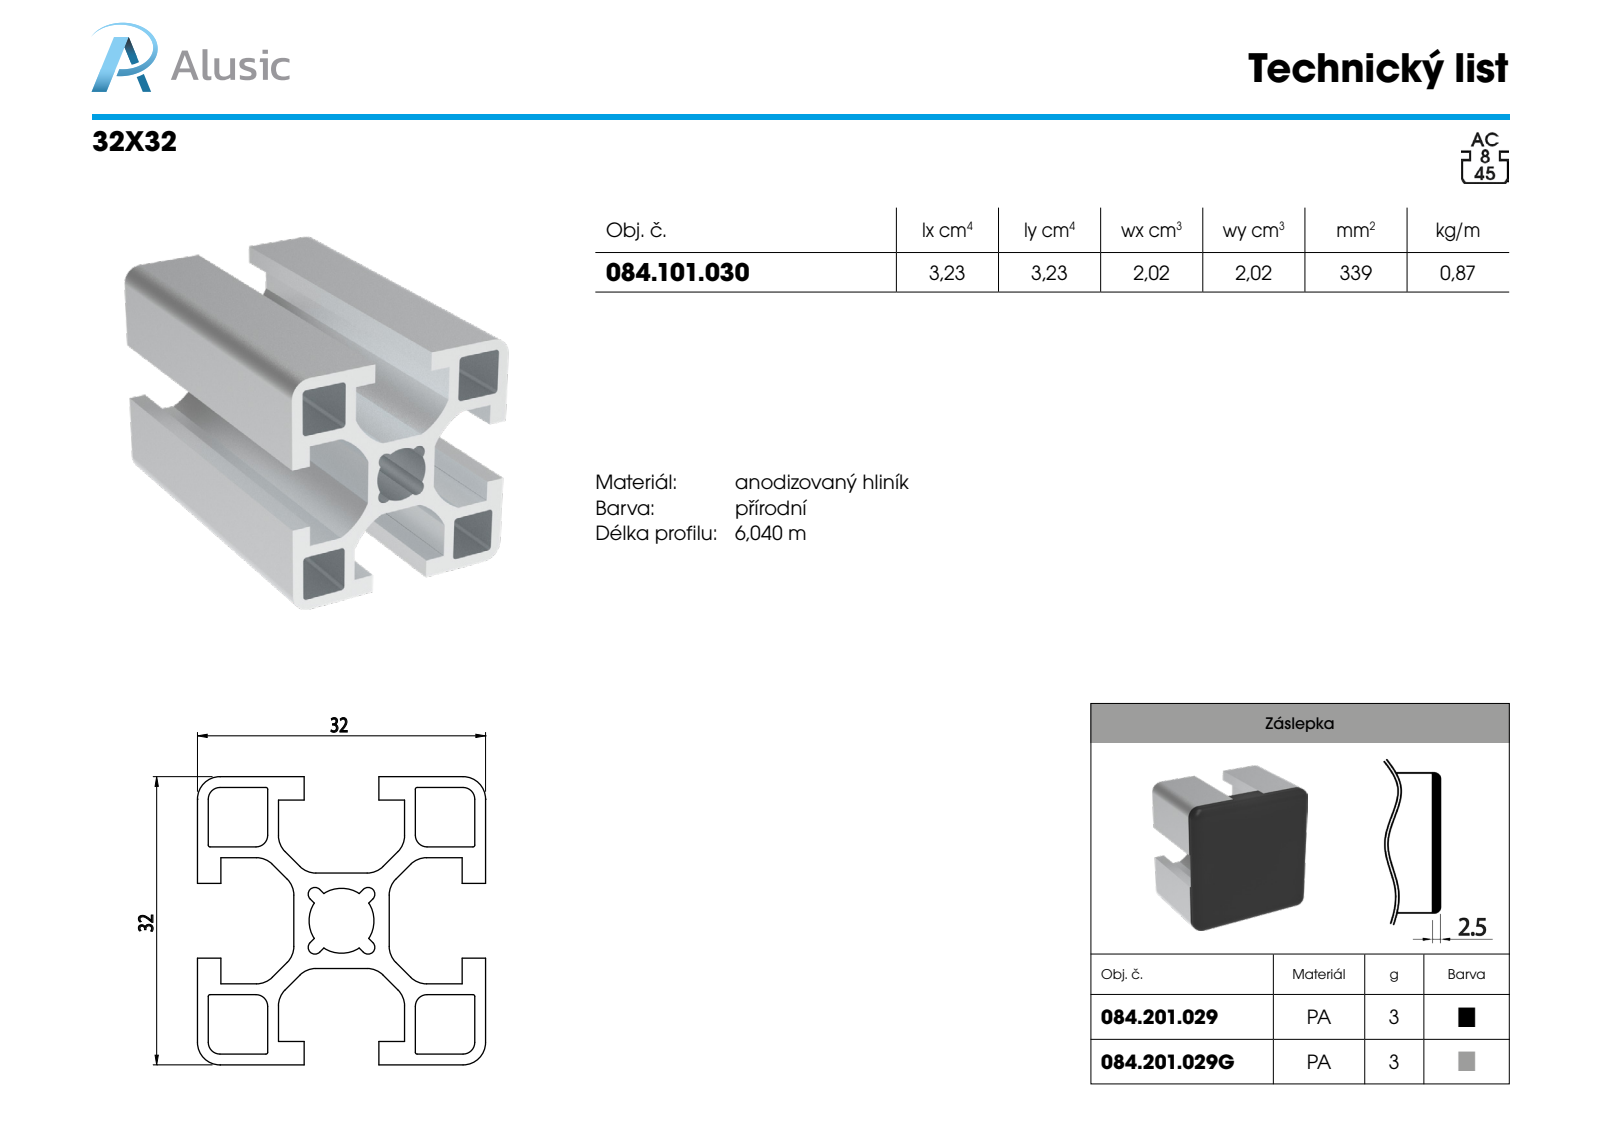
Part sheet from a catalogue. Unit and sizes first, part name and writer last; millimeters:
Units: millimetres
Overall size (bounding box): 100 × 32 × 32
Partial cylindrical surfaces — rounded edges, fillets, slot ends (radius × count): R0.5 ×16, R8.25 ×8, R1 ×4, R2.5 ×4, R3.65 ×1
Main face-to-face distances: 7.6, 1.5, 22.9, 24.4, 30.5, 6.1, 32, 9.1, 21.4, 15.3
Volume: 31 996 mm³ · Surface area: 36 578 mm²
Bodies: 1 solid, 93 faces (54 planar, 39 cylindrical, 0 other)
Part name (STEP PRODUCT): 084.101.030
STEP written by: SolidWorks 2018 (AUTOMOTIVE_DESIGN)
